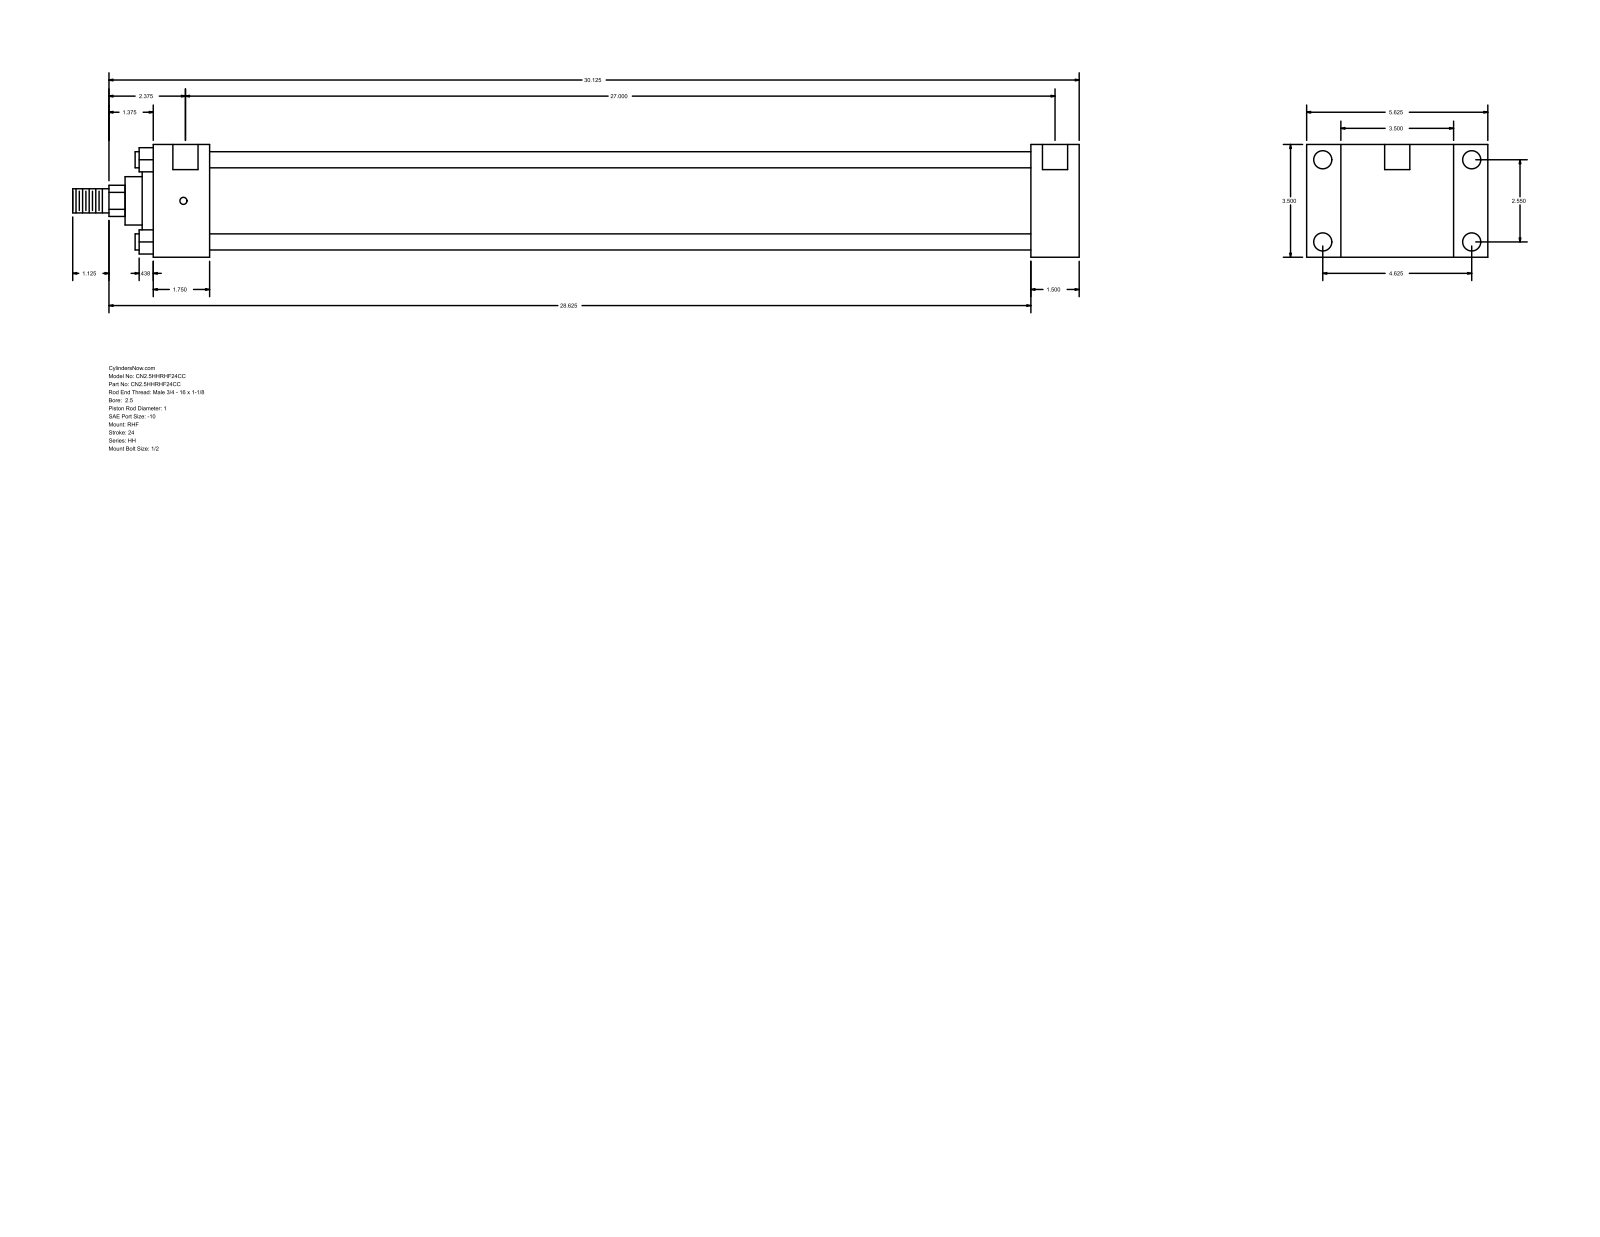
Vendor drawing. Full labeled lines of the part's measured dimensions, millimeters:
Part name (STEP PRODUCT): HH_RHF__0250_1
STEP written by: GSSL Pune (CONFIG_CONTROL_DESIGN)
Units: millimetres
Bodies: 0 solids, 90 faces (61 planar, 29 cylindrical, 0 other)
Overall size (bounding box): 793.75 × 142.88 × 88.9
Round holes (diameter × count): ⌀5.56 ×4, ⌀14.3 ×4, ⌀19.84 ×2
Round bosses / shafts (diameter × count): ⌀12.7 ×4, ⌀73.03 ×1, ⌀60.33 ×1, ⌀38.1 ×1, ⌀25.4 ×1, ⌀19.05 ×1
Partial cylindrical surfaces — rounded edges, fillets, slot ends (radius × count): R12.29 ×1
Main face-to-face distances: 88.9, 38.09, 26.99, 115.89, 692.16, 730.25, 142.88, 44.46, 647.7, 685.79
Hole centre spacings: 1.59, 64.76, 117.48, 134.15, 687.38, 688.97, 685.79
